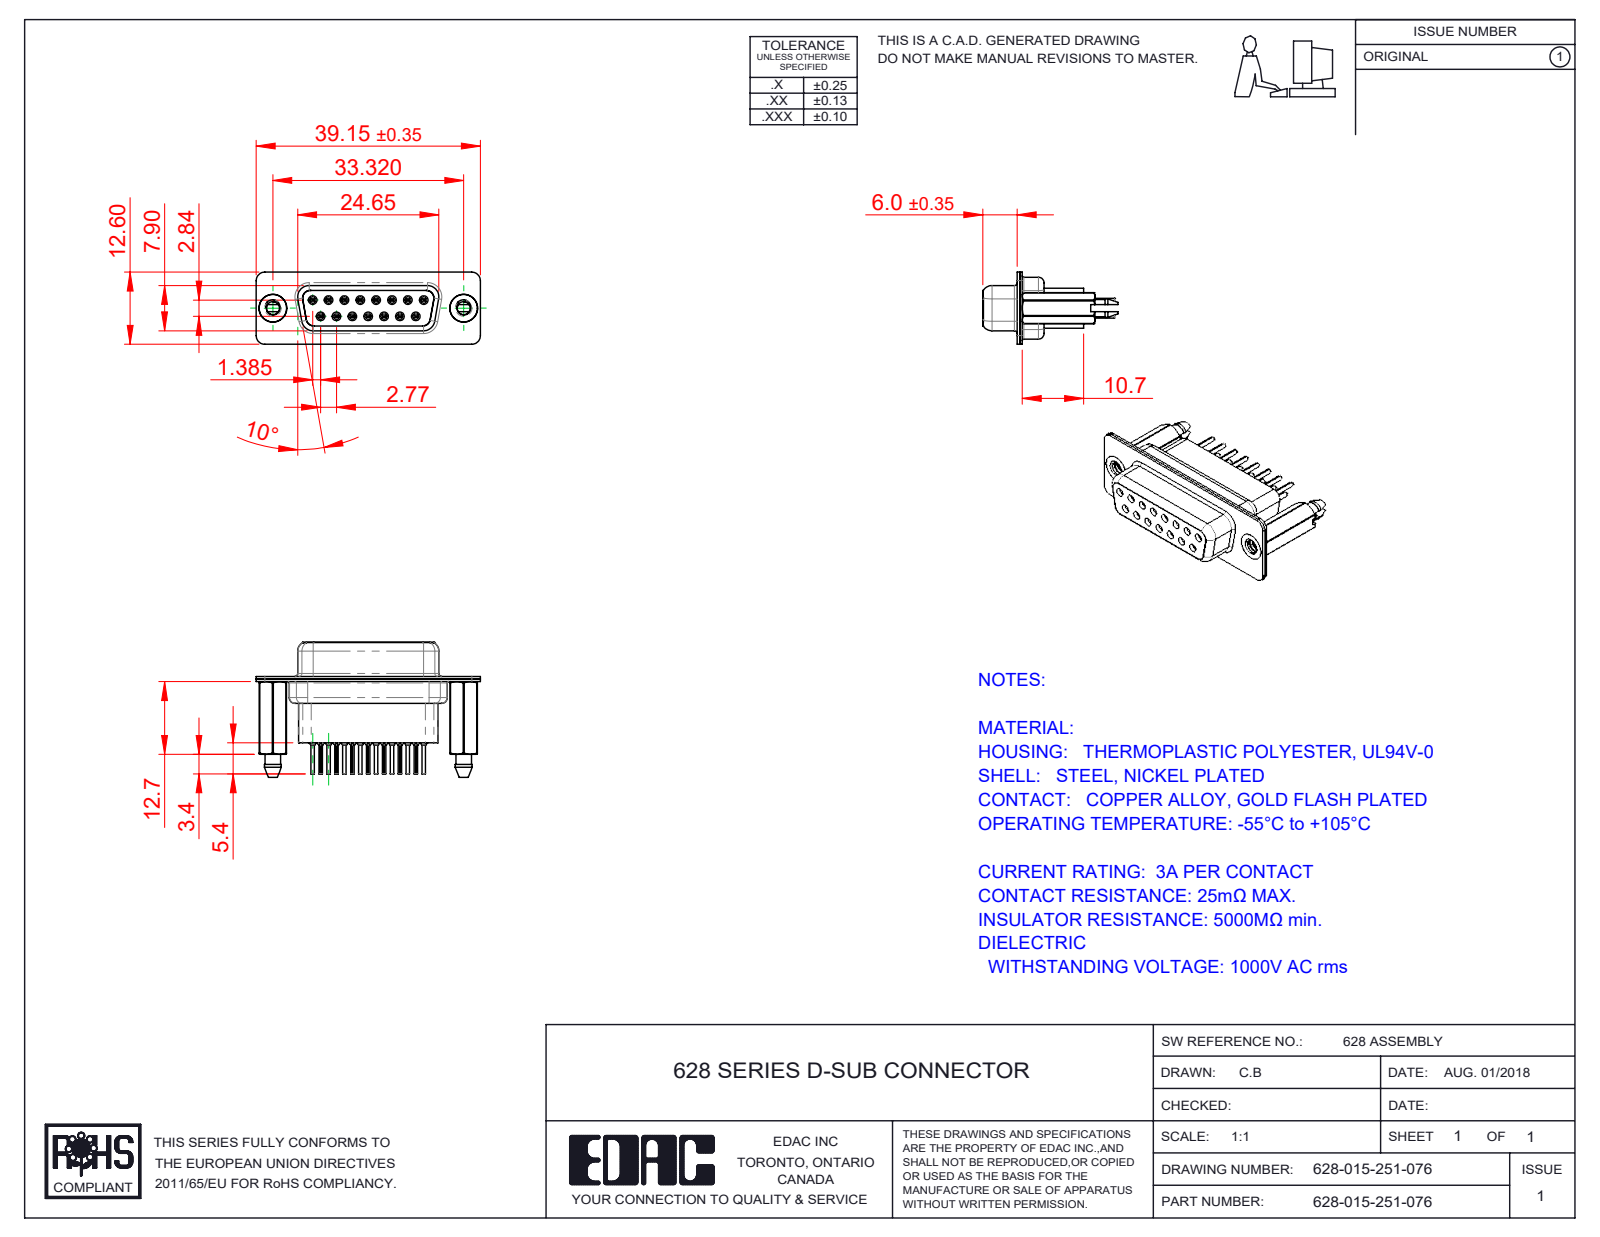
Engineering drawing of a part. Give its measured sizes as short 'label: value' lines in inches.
name: 628-015-251-076; 628 Contact Row 2_51; 628 Shell Front_15 Contacts; 628 Housing_15 HP (+3 more)
written by: SolidWorks 2020 (CONFIG_CONTROL_DESIGN)
unit: in
bodies: 20 solids, 2198 faces (564 planar, 664 cylindrical, 970 other)
size: 1.541 × 0.929 × 0.496
volume: 0.22 in³; area: 12.86 in²
holes: 15× ⌀0.008, 15× ⌀0.031, 15× ⌀0.035, 15× ⌀0.043, 15× ⌀0.063, 8× ⌀0.067, 2× ⌀0.089, 2× ⌀0.157, 2× ⌀0.159, 2× ⌀0.191
bosses: 15× ⌀0.079, 15× ⌀0.059, 15× ⌀0.047, 15× ⌀0.024, 2× ⌀0.195, 2× ⌀0.189
rounds: 30× R0.004, 20× R0.059, 15× R0.011, 12× R0.079, 8× R0.053, 6× R0.063, 4× R0.01, 4× R0.02
face distances: 0.018, 0.016, 0.26, 0.035, 0.335, 0.075, 0.276, 0.187, 0.055, 0.033
hole spacings: 0.124, 0.109, 0.218, 0.327, 0.436, 0.198, 0.198, 0.294
